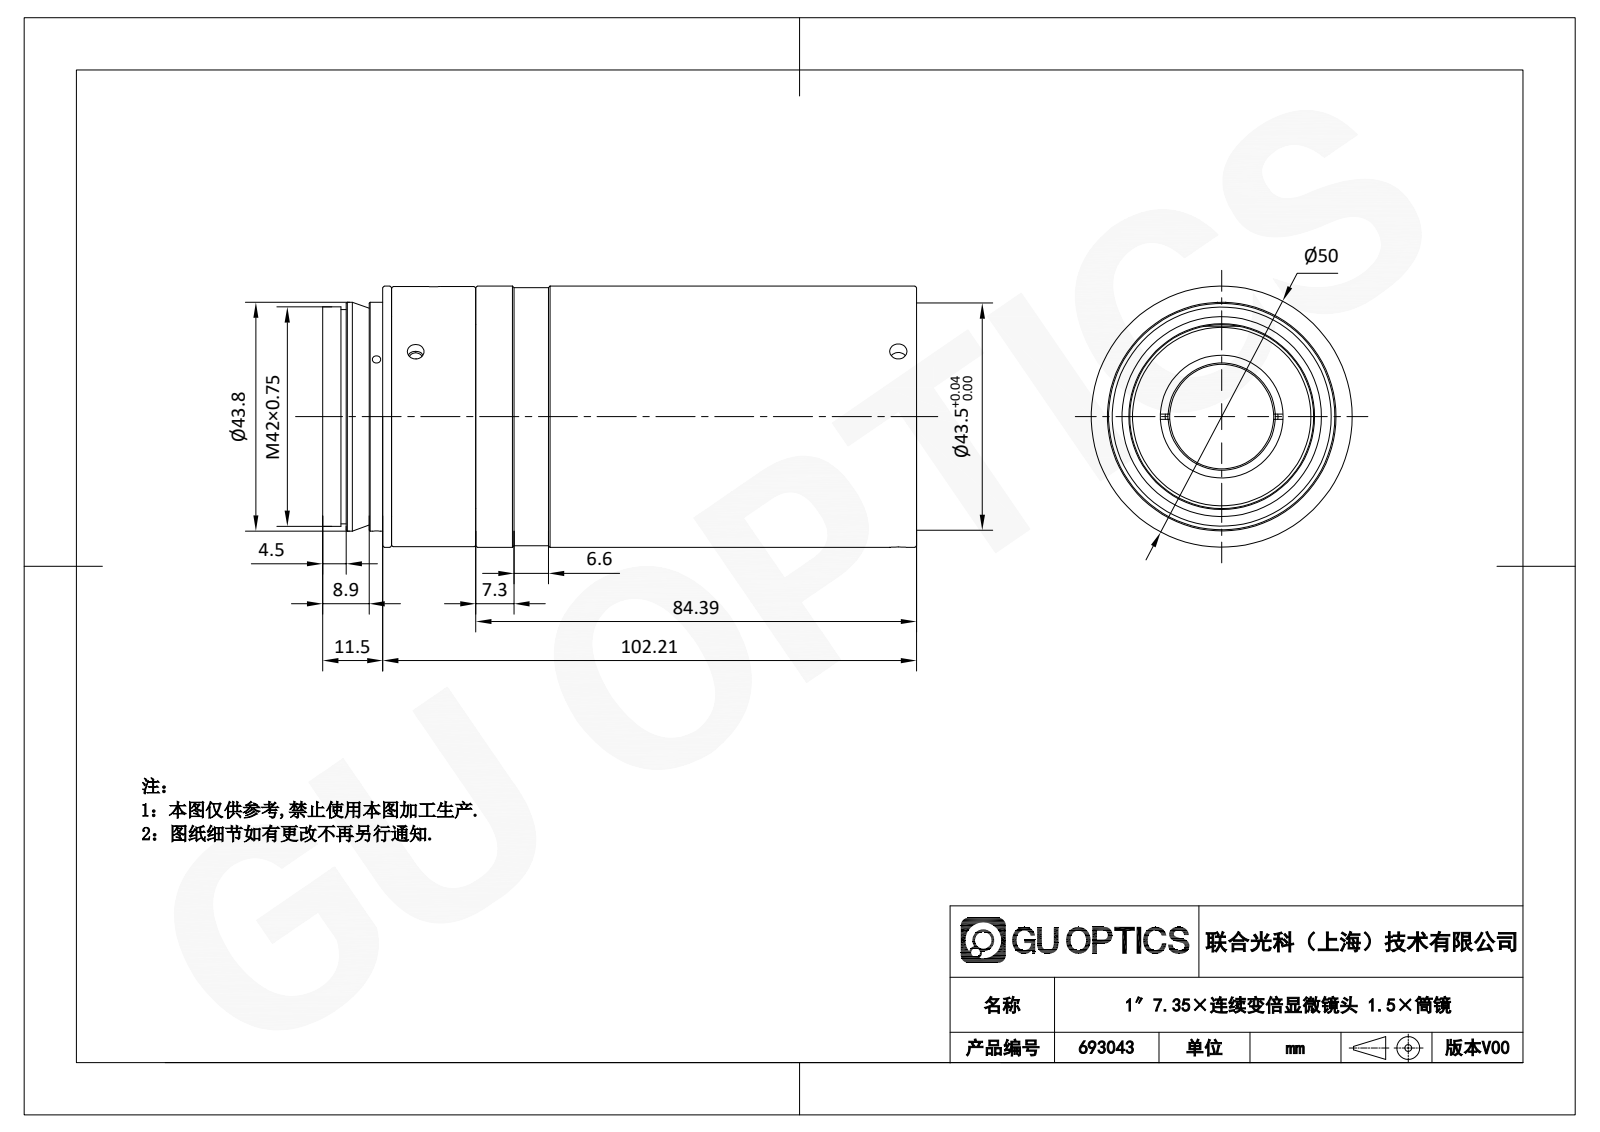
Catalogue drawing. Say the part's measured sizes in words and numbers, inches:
The part is named "693043". Its 3-D file was written by "SolidWorks 2020 (CONFIG_CONTROL_DESIGN)". It is 0 solids with 97 faces: 30 planar, 32 cylindrical and 35 other. Overall it measures 4.477 by 1.969 by 1.969 inches. Round holes: 3 of diameter 0.13, 2 of diameter 0.098, 2 of diameter 0.126, 1 of diameter 0.106, 1 of diameter 1.614, 1 of diameter 1.654, 1 of diameter 1.713, 1 of diameter 1.724. Round bosses or shafts: 3 of diameter 0.063, 1 of diameter 1.969, 1 of diameter 1.961, 1 of diameter 1.945, 1 of diameter 1.756, 1 of diameter 1.506, 1 of diameter 1.496, 1 of diameter 1.493. The main face-to-face distances are 0.143, 0.048, 0.095, 0.191, 0.133, 4.024, 4.157, 0.413, 3.611, 3.743. The hole center spacings are 3.638, 3.502.
